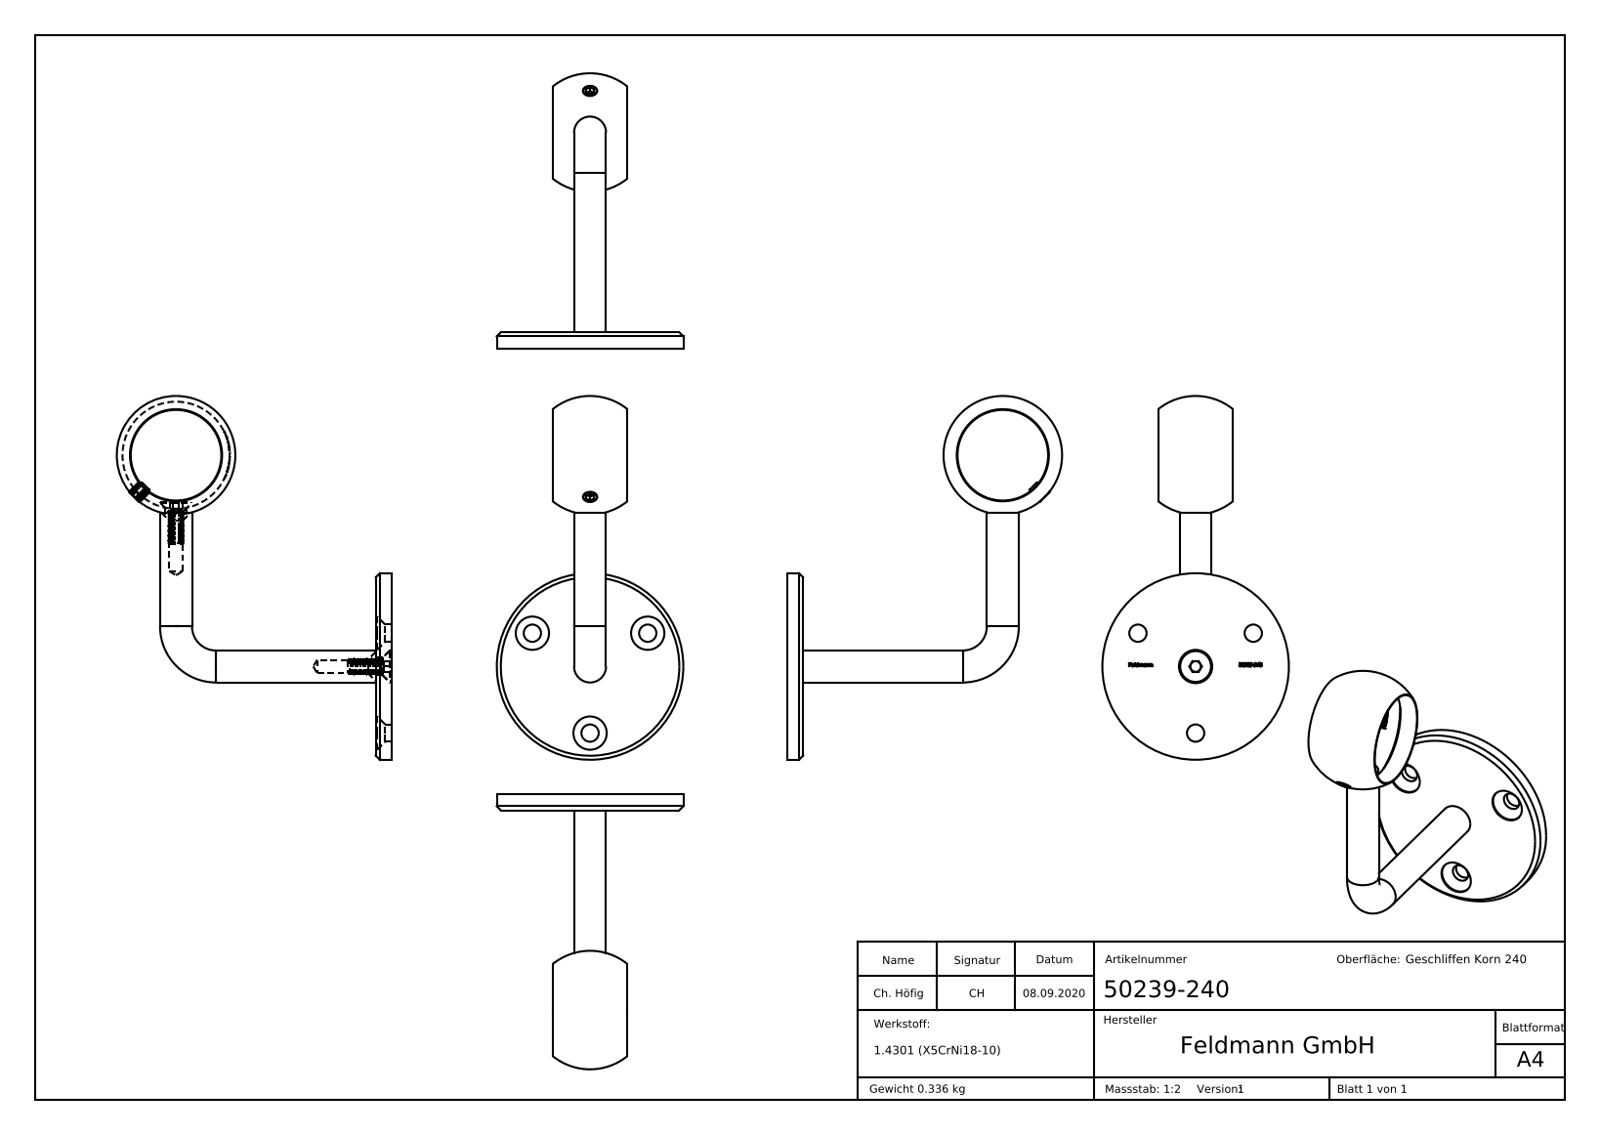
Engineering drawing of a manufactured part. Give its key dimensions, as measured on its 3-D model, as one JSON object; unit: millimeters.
{"part_name": "50242-240_50242-240; socket countersunk head screw_din; 5024X-240 Teil1; socket set screw flat point_din (+7 more)", "step_written_by": "SolidWorks 2018 (CONFIG_CONTROL_DESIGN)", "units": "millimeters", "bodies": {"solids": 6, "faces": 631, "planar": 257, "cylindrical": 73, "other": 301}, "overall_size": [136.56, 103.25, 70], "volume_mm3": 43556, "surface_area_mm2": 23706, "round_holes": [[6.5, 4], [12.5, 4], [5, 3], [8, 1], [34, 1], [40.2, 1]], "round_bosses_or_shafts": [[6, 3], [12, 2], [11.57, 2], [70, 1]], "partial_cylinders_radius": [[20.2, 1]], "face_to_face_distances": [6, 0.45, 5.55, 16, 4.02, 28, 16.45, 10.45, 11.95, 4.05], "hole_center_spacings": [25, 43.3]}
